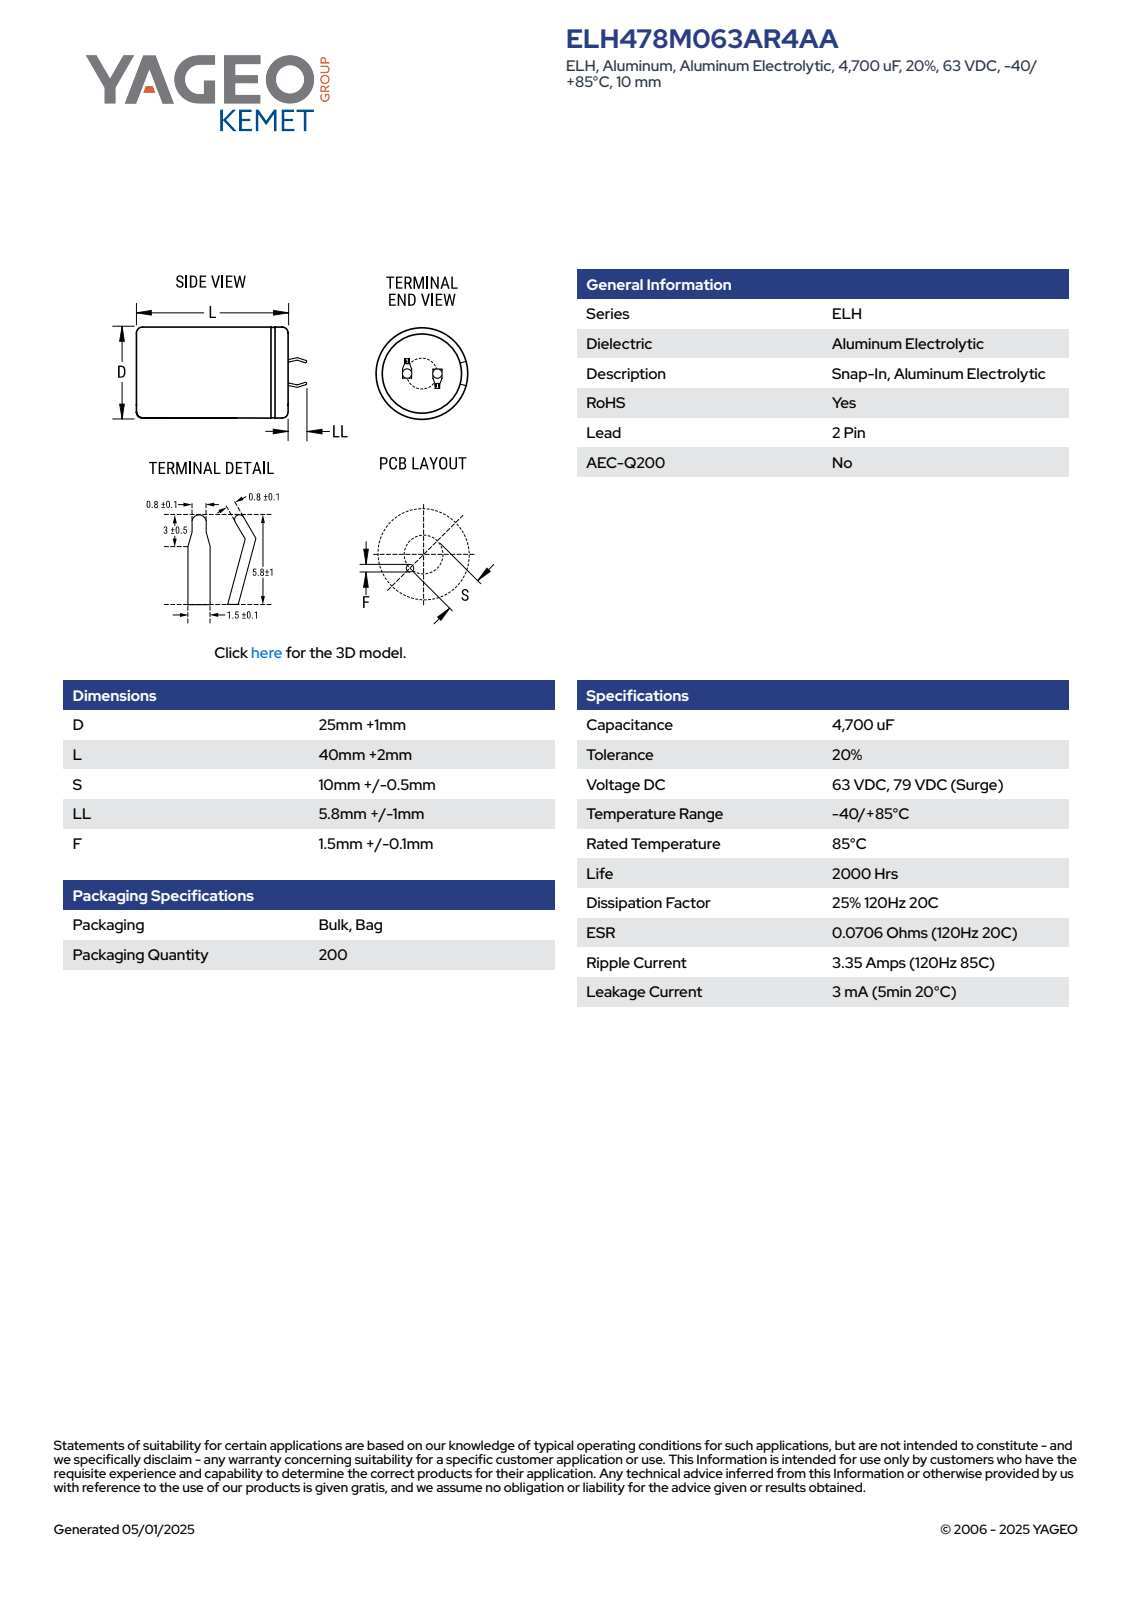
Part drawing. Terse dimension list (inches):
name: CARS_K2P_25X40_D26L42S10LL6.8F1.6
written by: SolidWorks 2014 (AUTOMOTIVE_DESIGN)
unit: in
bodies: 1 solid, 100 faces (52 planar, 9 cylindrical, 39 other)
size: 1.921 × 1.024 × 1.024
volume: 1.349 in³; area: 6.992 in²
holes: 1× ⌀0.906
bosses: 1× ⌀1.024
rounds: 1× R0.511
face distances: 1.653, 0.024, 1.673, 0.02, 0.279, 0.3, 0.03, 0.053, 0.302, 0.255
